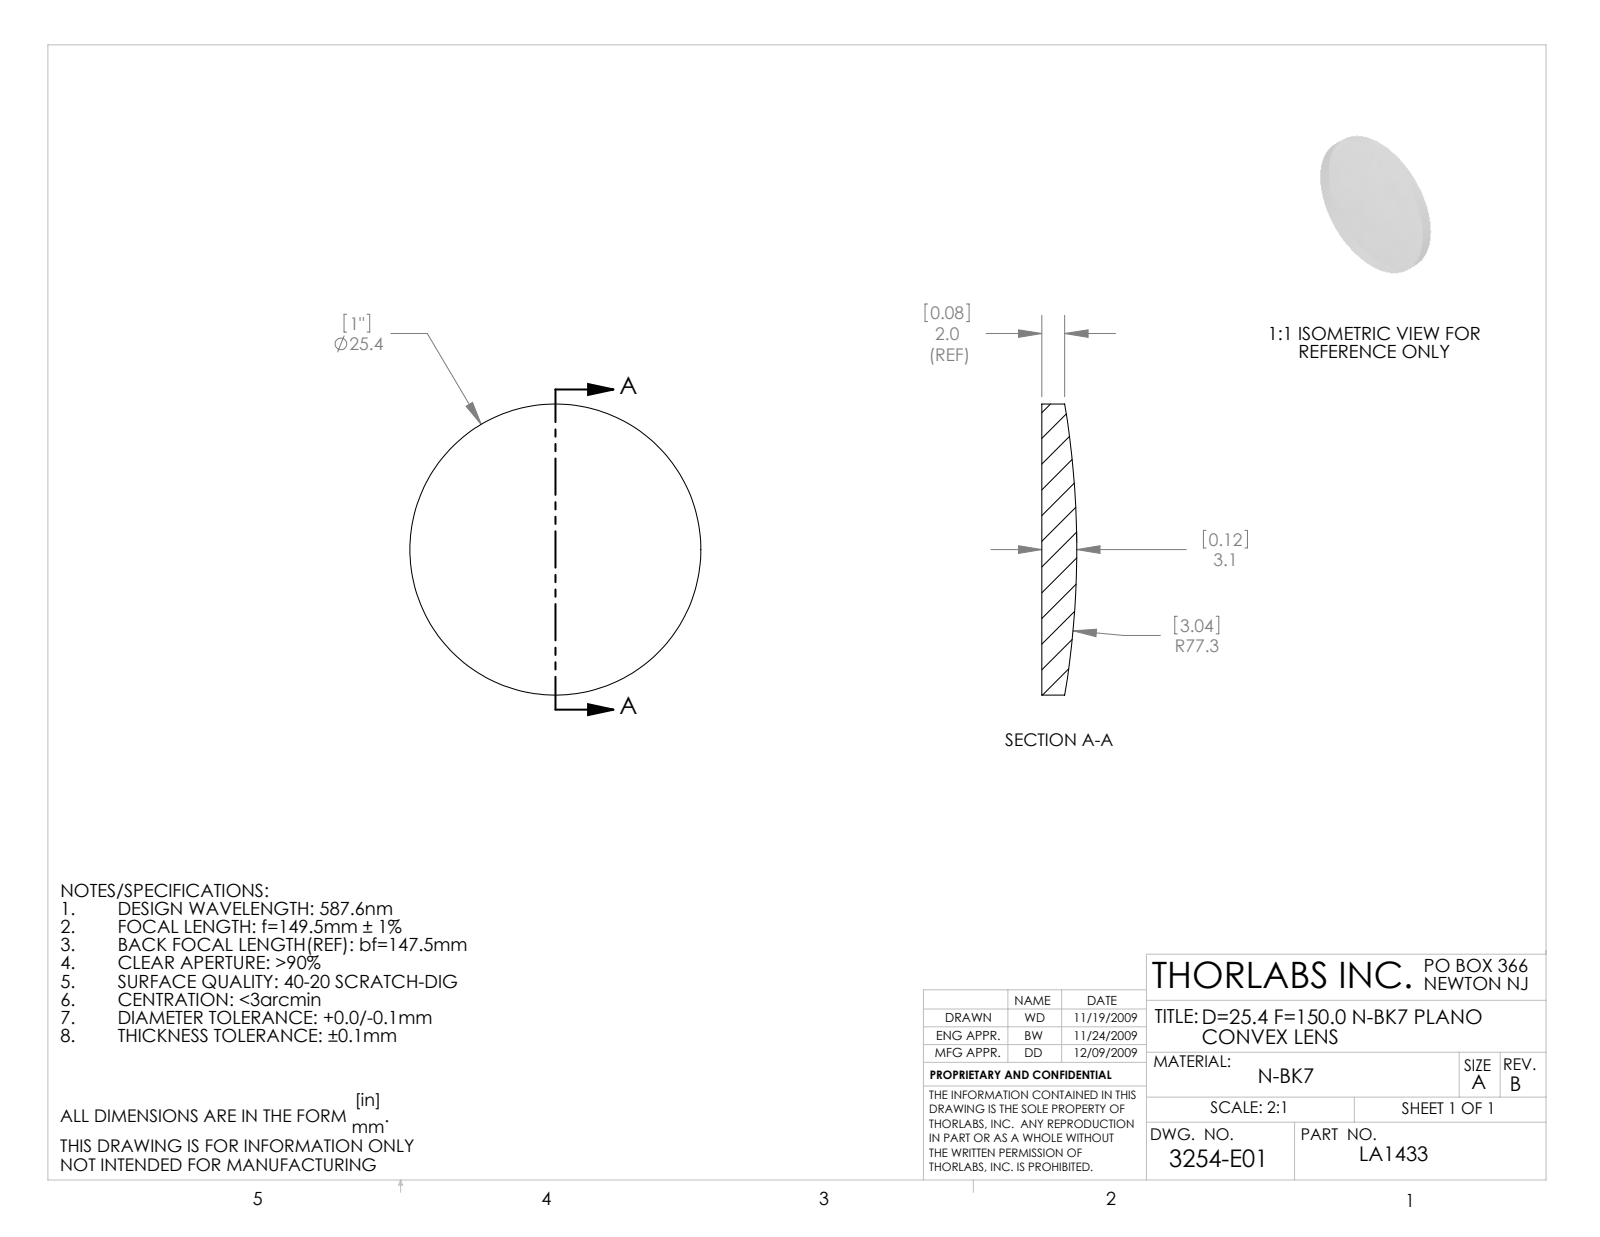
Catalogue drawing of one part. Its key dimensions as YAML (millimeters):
part_name: "3254-E0W"
step_written_by: "SolidWorks 2009 (AUTOMOTIVE_DESIGN)"
units: millimeters
bodies: {solids: 1, faces: 5, planar: 1, cylindrical: 2, other: 2}
overall_size: [25.4, 25.4, 3.05]
volume: 1280
surface_area: 1176
round_bosses_or_shafts:
  - {diameter: 25.4, count: 1}
